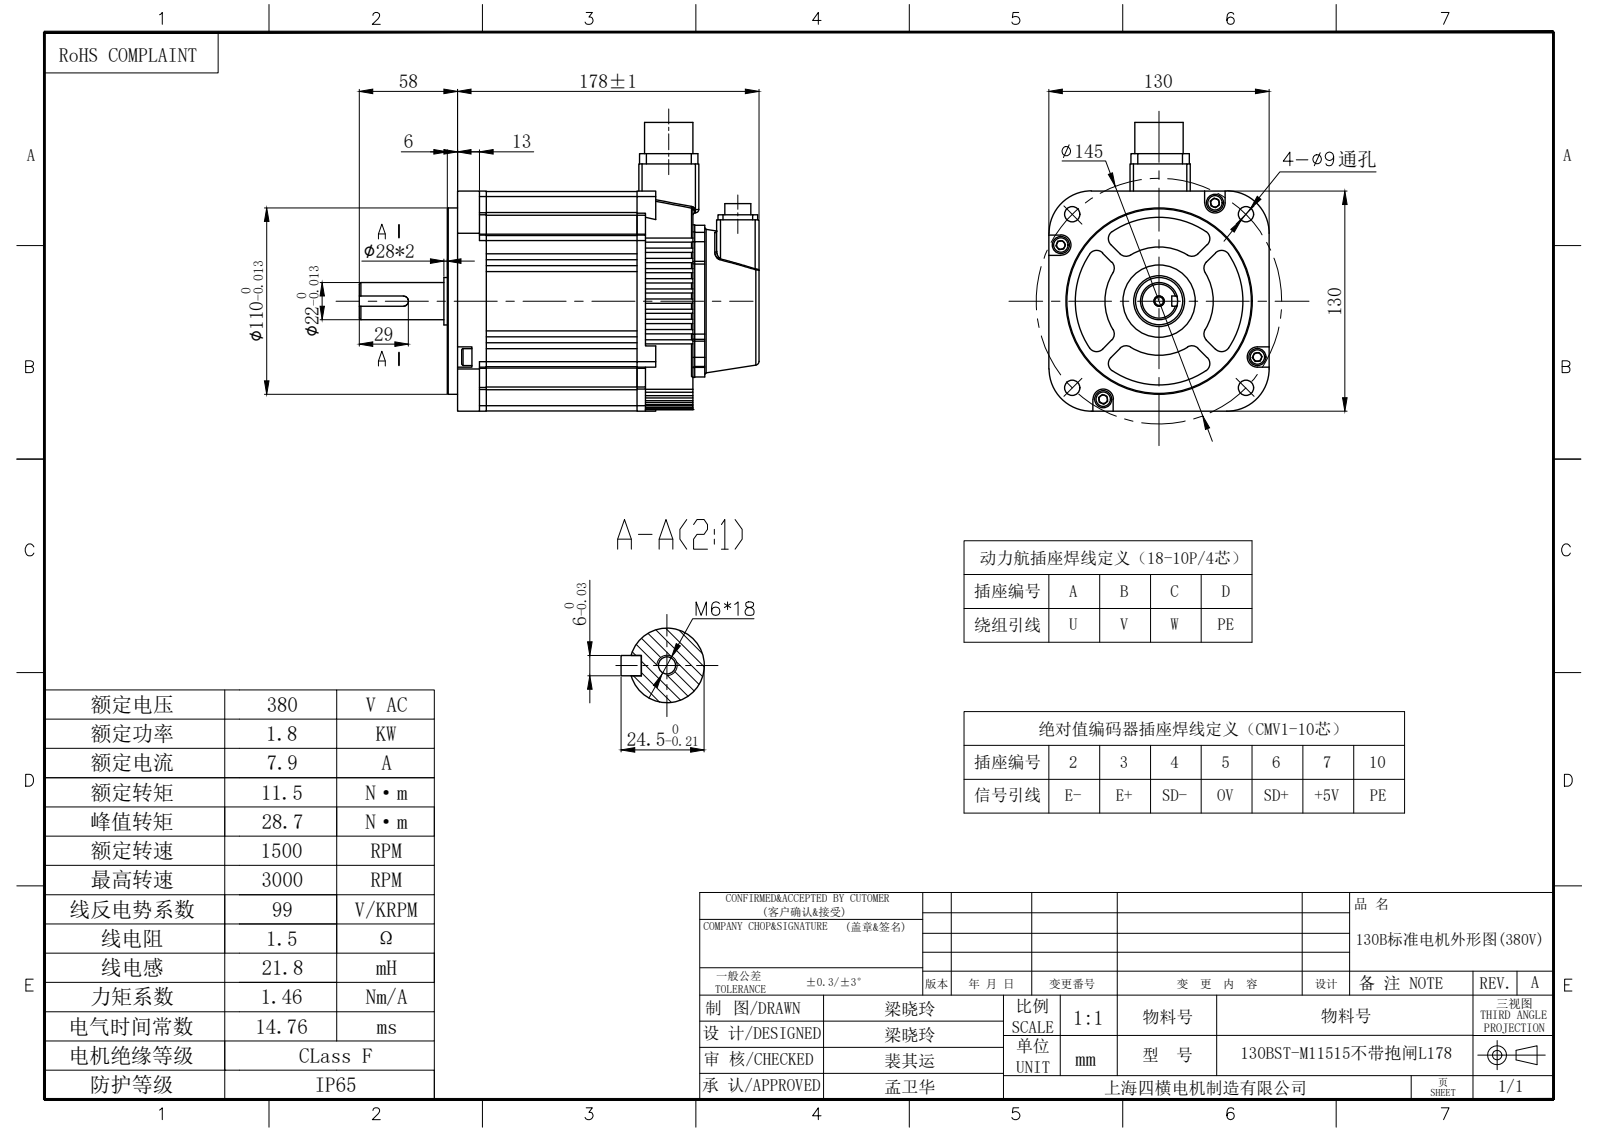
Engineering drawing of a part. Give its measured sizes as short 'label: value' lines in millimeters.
name: 130BST机身89; 130BST后端盖02; 130BST前端盖出轴; 130BST后盖 (+2 more)
written by: SolidWorks 2020 (AUTOMOTIVE_DESIGN)
unit: mm
bodies: 44 solids, 798 faces (387 planar, 332 cylindrical, 79 other)
size: 236 × 170.5 × 130
volume: 2 244 000 mm³; area: 229 535 mm²
holes: 8× ⌀3, 8× ⌀6.6, 5× ⌀5, 4× ⌀9, 1× ⌀11.5, 1× ⌀24, 1× ⌀42.6
bosses: 4× ⌀10, 4× ⌀6, 4× ⌀2.5, 1× ⌀110, 1× ⌀30, 1× ⌀28.5, 1× ⌀28, 1× ⌀22
rounds: 16× R1.5, 16× R3.25, 16× R5, 15× R2, 13× R3, 8× R3.5, 4× R2.25, 4× R2.5
face distances: 89, 122, 33, 106, 17, 139, 129.5, 3.5, 26, 103.75
hole spacings: 1.34, 12.02, 17, 27, 47.91, 66.73, 68, 94.37
